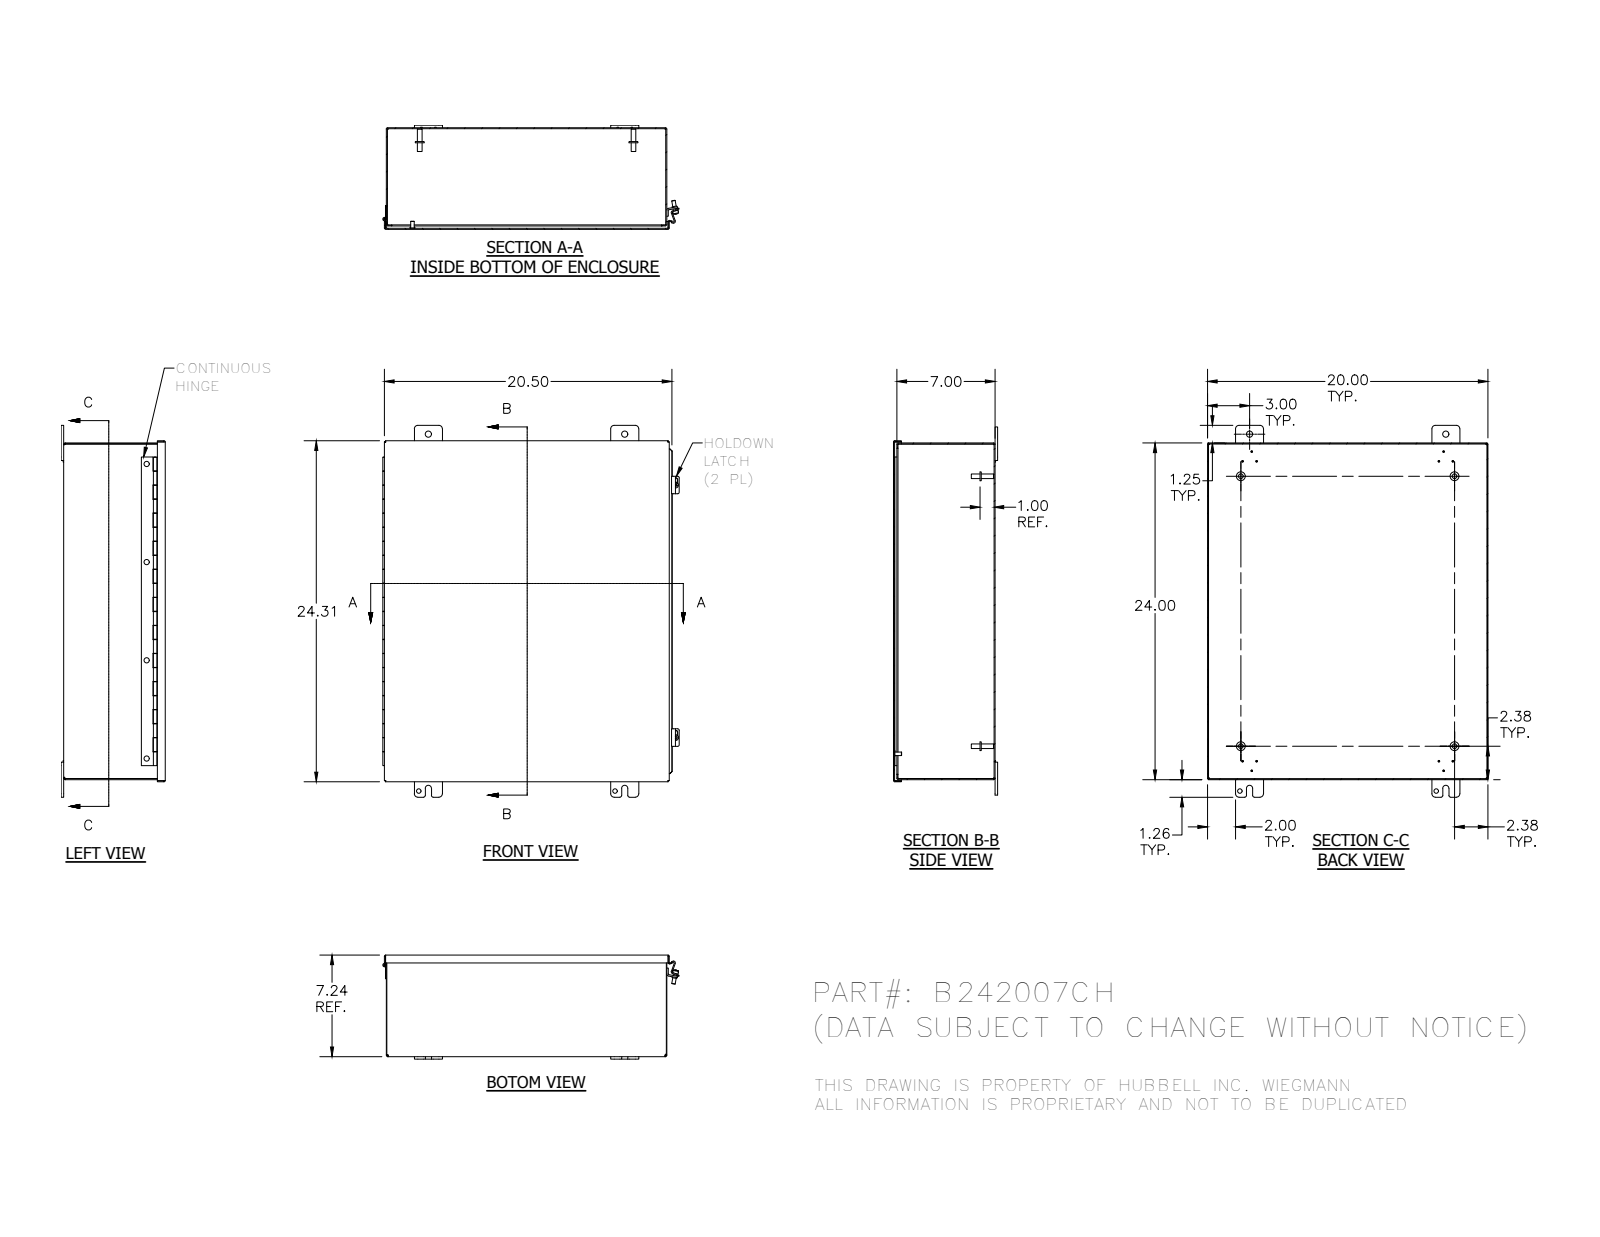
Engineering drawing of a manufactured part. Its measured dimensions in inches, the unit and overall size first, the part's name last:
Units: inches
Overall size (bounding box): 26.505 × 21.136 × 7.423
Round holes (diameter × count): ⌀0.11 ×4, ⌀0.313 ×4, ⌀0.375 ×4, ⌀0.438 ×4, ⌀0.196 ×2, ⌀0.125 ×1, ⌀0.125 ×1
Round bosses / shafts (diameter × count): ⌀0.625 ×4, ⌀0.33 ×4, ⌀0.25 ×4, ⌀0.41 ×2, ⌀0.344 ×2, ⌀0.337 ×1, ⌀0.12 ×1
Partial cylindrical surfaces — rounded edges, fillets, slot ends (radius × count): R0.125 ×16, R0.25 ×16, R0.031 ×8, R0.063 ×8, R0.07 ×8, R0.105 ×8, R0.016 ×5, R0.09 ×5
Main face-to-face distances: 0.074, 7.169, 7.243, 7.095, 19.926, 23.926, 20, 19.852, 24, 23.852
Hole centre spacings: 14, 1.593, 7, 18, 24.005, 27.789, 0.75, 13.39
Volume: 129.3 in³ · Surface area: 3 484 in²
Bodies: 20 solids, 649 faces (395 planar, 185 cylindrical, 69 other)
Part name (STEP PRODUCT): B242007CH; B242007CHBKP; B2420CHLID; H6010101 (+8 more)
STEP written by: Autodesk Inventor 2012 (AUTOMOTIVE_DESIGN)
